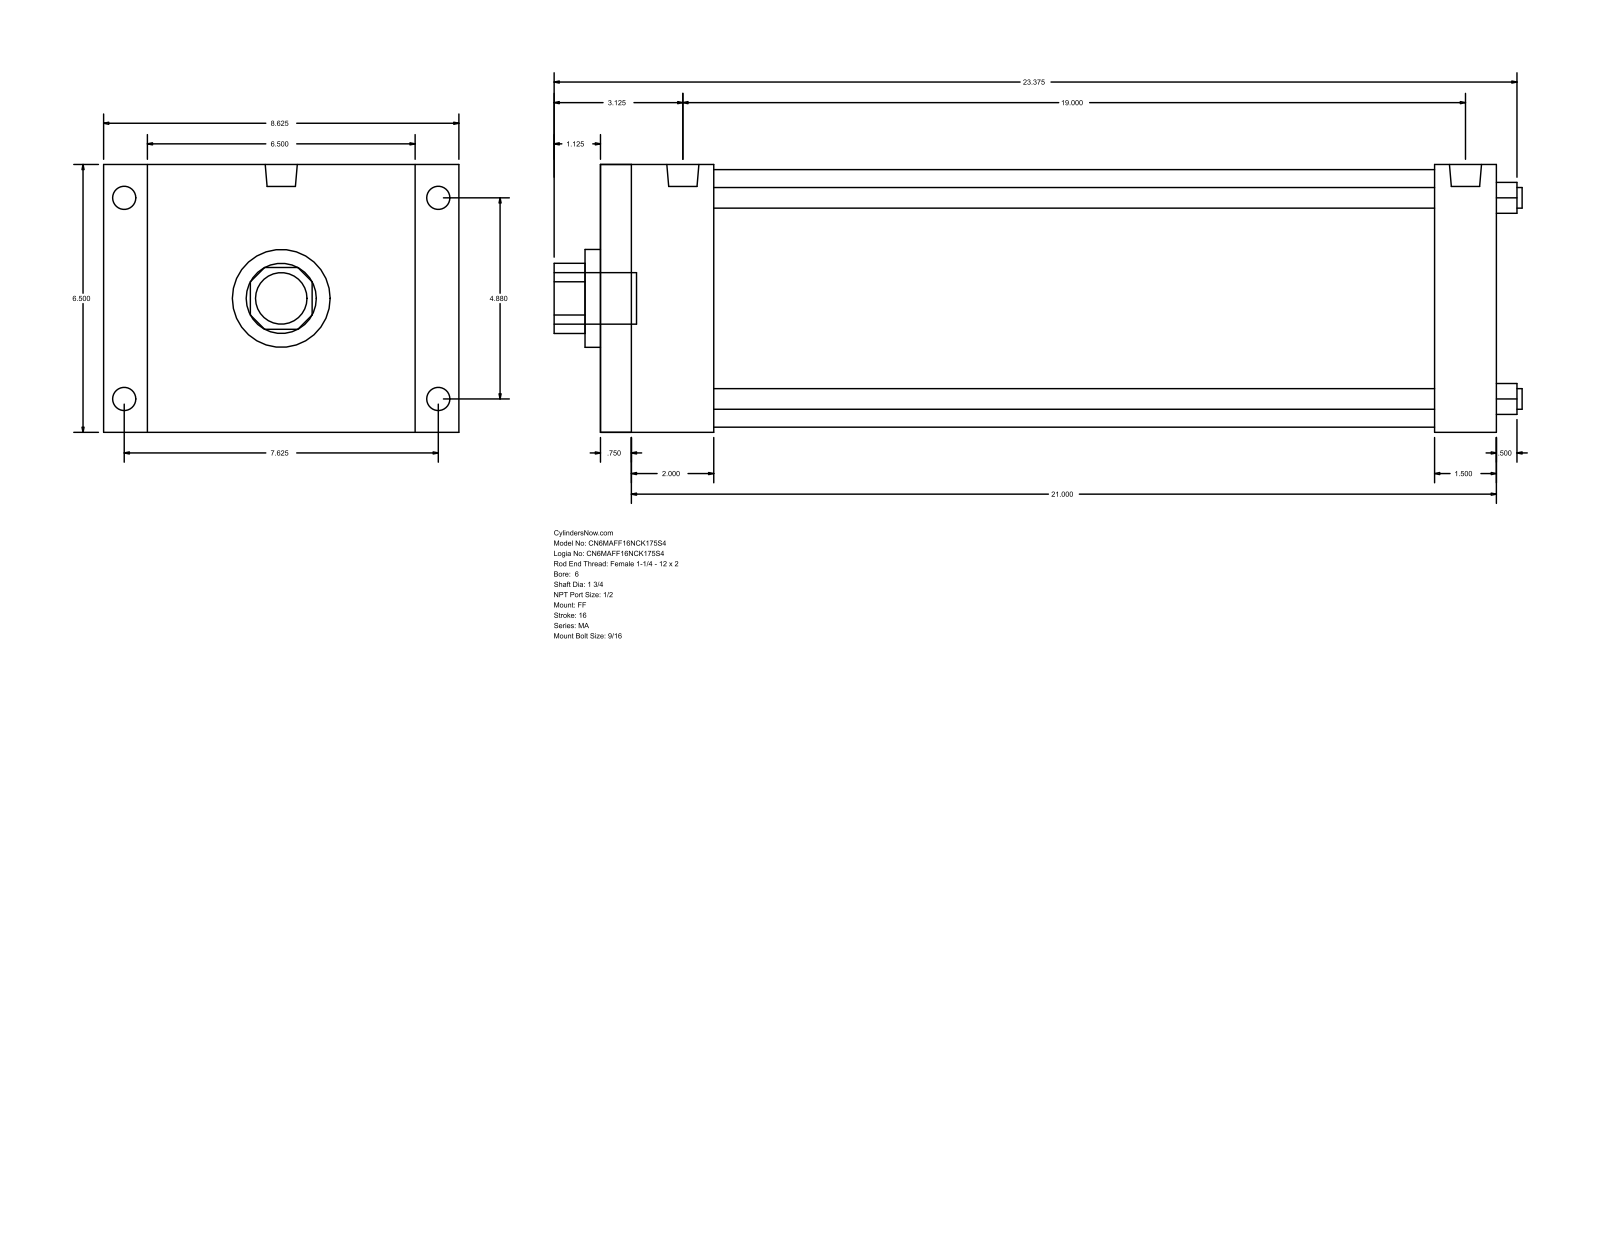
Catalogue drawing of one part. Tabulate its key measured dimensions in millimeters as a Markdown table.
| quantity | value |
| --- | --- |
| part name | MA_FF__0600_1.75 |
| STEP written by | GSSL Pune (CONFIG_CONTROL_DESIGN) |
| units | millimeters |
| bodies | 0 solids, 92 faces (64 planar, 28 cylindrical, 0 other) |
| overall size | 596.9 × 219.07 × 165.1 |
| round holes (diameter × count) | 12.7 × 4, 44.45 × 1, 60.33 × 1, 158.75 × 1 |
| round bosses / shafts (diameter × count) | 17.46 × 4, 14.29 × 4, 19.77 × 2, 31.75 × 1 |
| partial cylindrical surfaces (radius × count) | 21.63 × 1 |
| main face-to-face distances | 165.1, 552.45, 19.05, 533.4, 38.1, 50.8, 69.85, 482.6, 514.35, 495.3 |
| hole center spacings | 87.65, 123.96, 175.31 |
